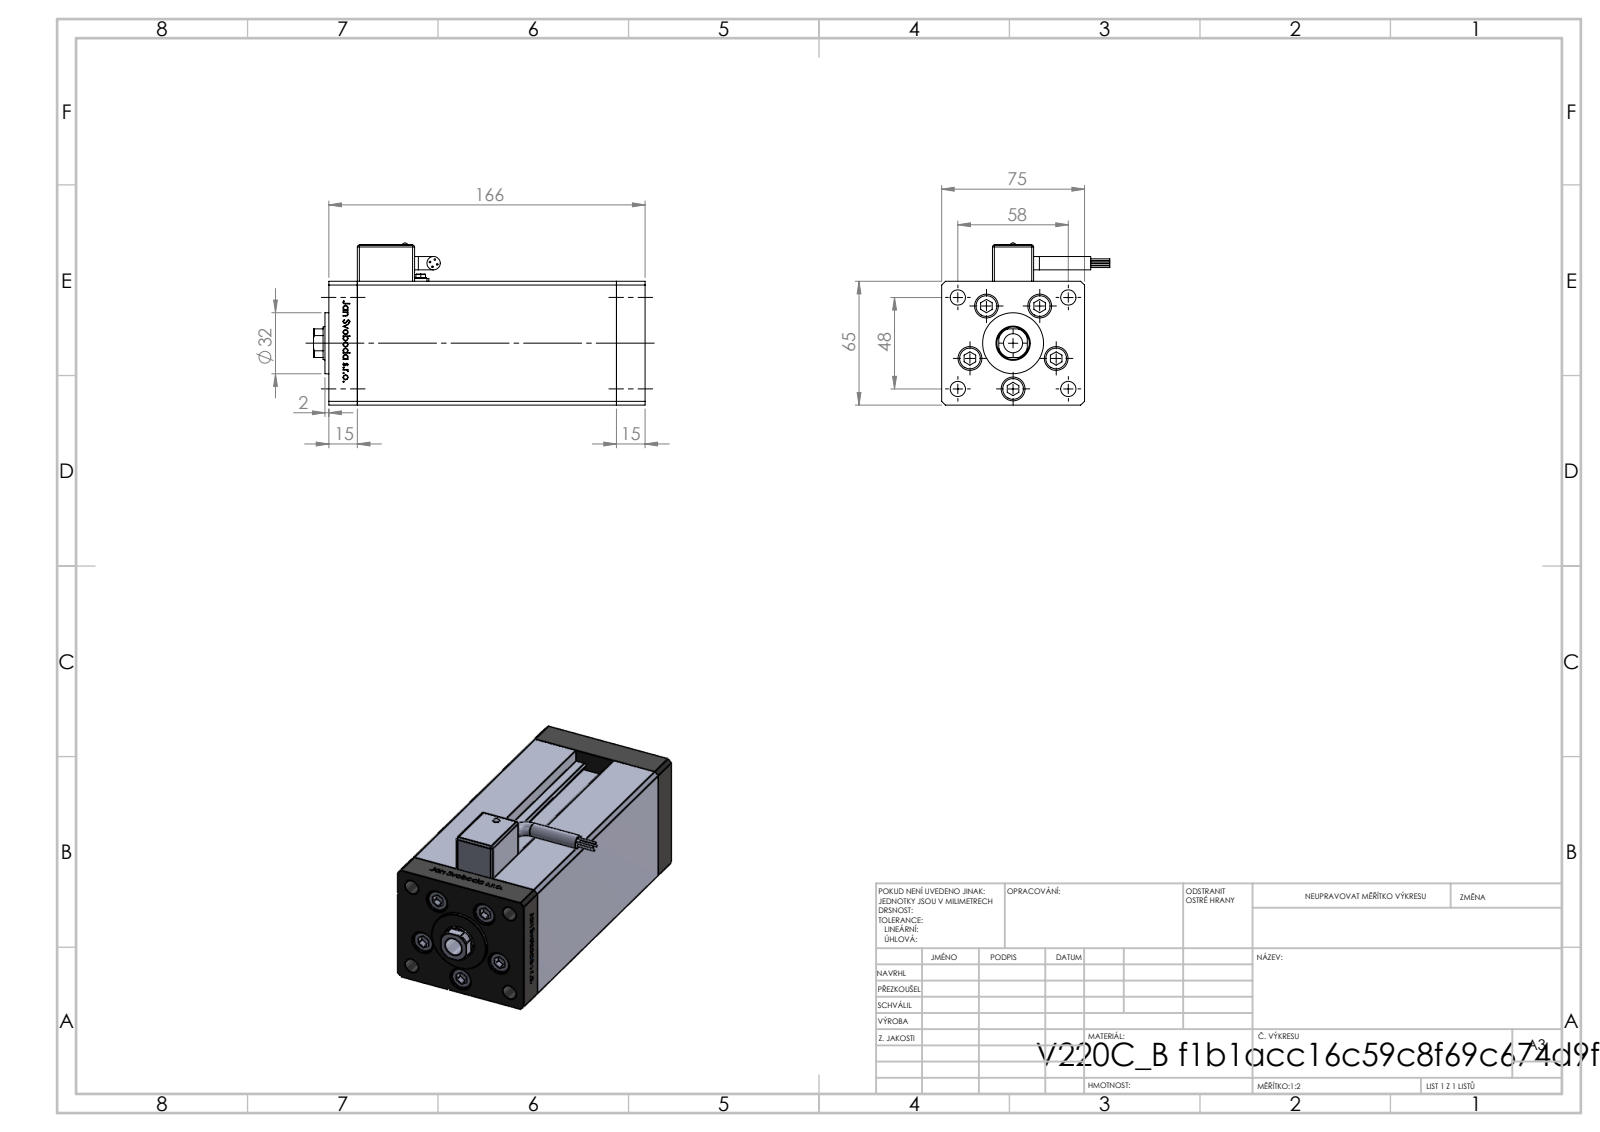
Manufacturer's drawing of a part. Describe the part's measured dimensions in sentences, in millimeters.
The part is named "Magnetic_Switch_MSU4; ALLEN BOLT; V220C_FRONT_B; V220C BACK_B (+2 more)". Its 3-D file was written by "SolidWorks 2019 (CONFIG_CONTROL_DESIGN)". It is 15 solids with 1277 faces: 499 planar, 188 cylindrical and 590 other. Overall it measures 174 by 88.3 by 85.1 millimeters. Its volume is 740 493 cubic millimeters and its surface area 131 255 square millimeters. Round holes: 5 of diameter 9, 5 of diameter 12.5, 4 of diameter 8, 2 of diameter 2, 2 of diameter 13.16, 1 of diameter 3.6, 1 of diameter 5, 1 of diameter 7, 1 of diameter 10, 1 of diameter 18. Round bosses or shafts: 5 of diameter 8, 4 of diameter 0.85, 2 of diameter 7, 1 of diameter 32, 1 of diameter 6, 1 of diameter 3.5, 1 of diameter 2.5. Partial cylindrical surfaces (rounded edges, fillets, slot ends): 14 of radius 1, 2 of radius 0.93, 2 of radius 4, 1 of radius 8.5. The main face-to-face distances are 75, 65, 136, 15, 151, 166, 54.5, 58.5, 6.5, 4. The hole center spacings are 24, 37.64, 15.67, 17.22, 27.71, 28.83, 29, 32.63.
